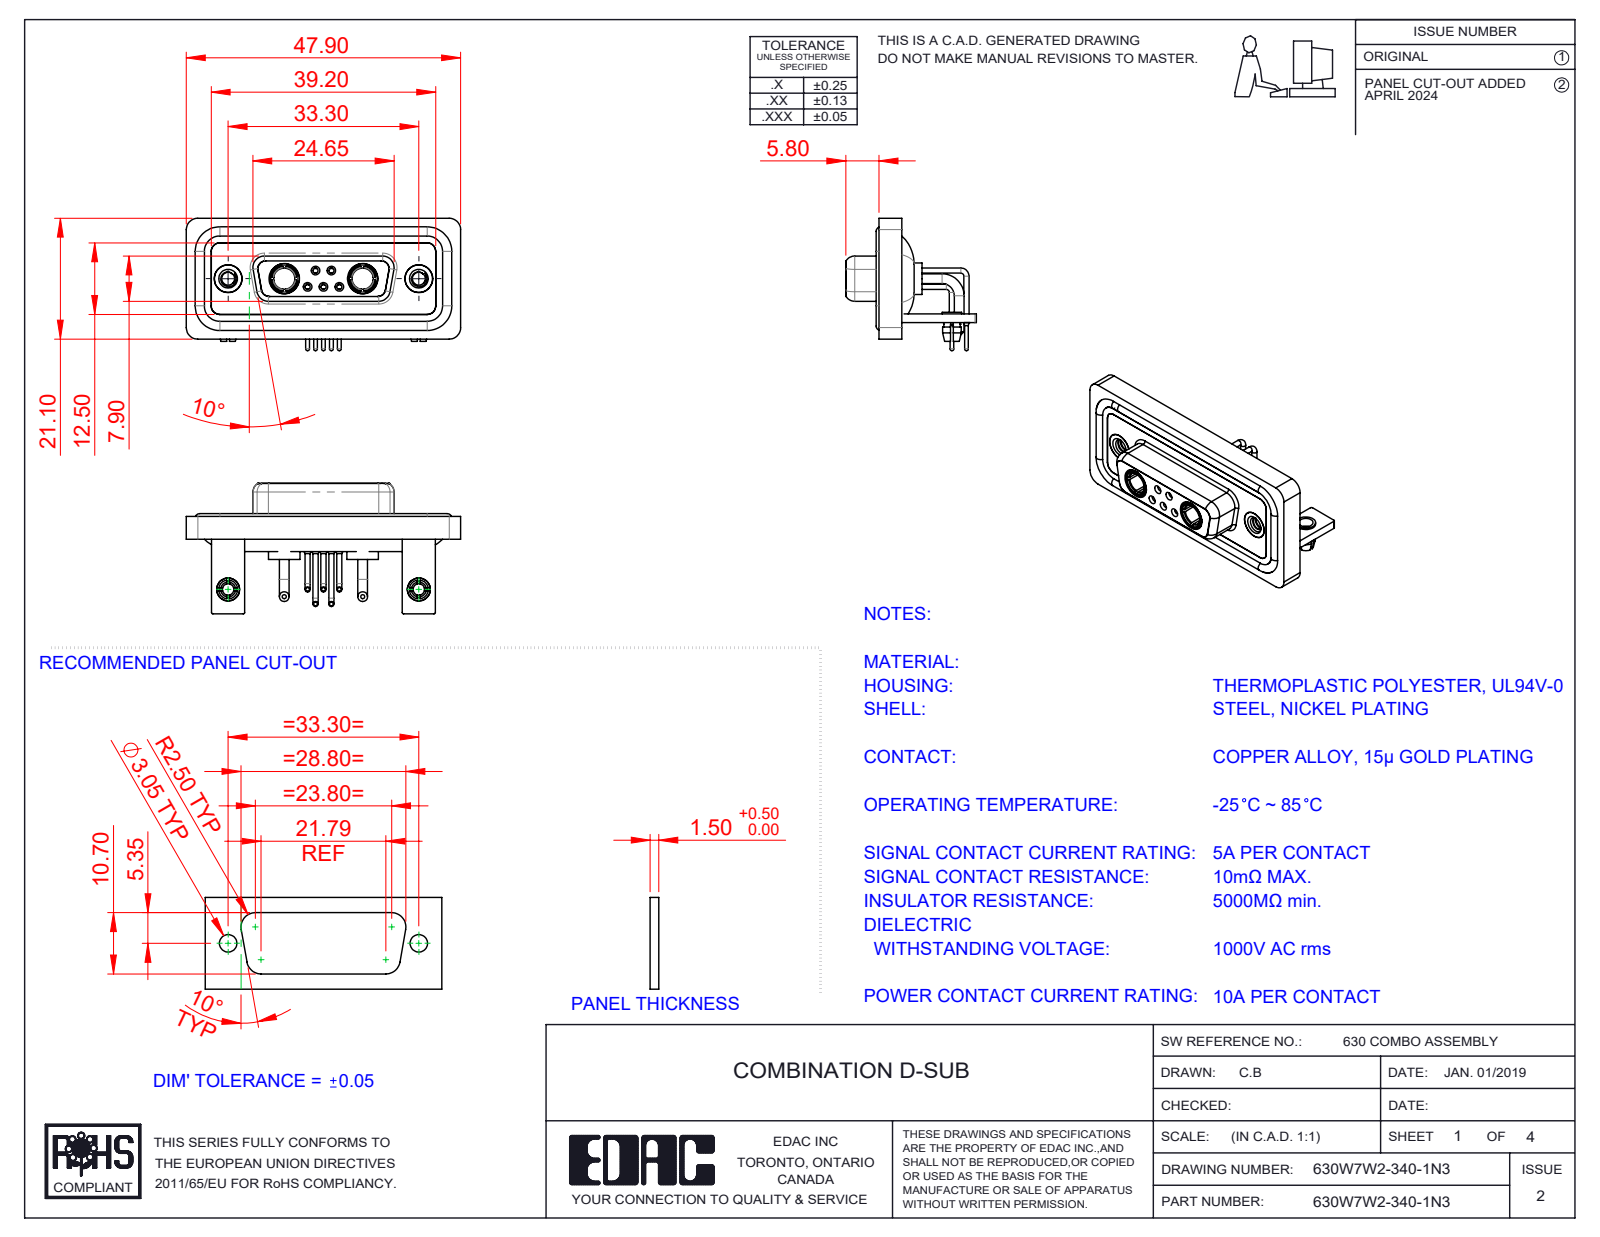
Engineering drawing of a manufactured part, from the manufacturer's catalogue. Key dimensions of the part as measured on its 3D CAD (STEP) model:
Part name (STEP PRODUCT): Power Socket_10A RA; 630Combo Contact Row 2_50 Contacts; 630Combo Housing_7W2; 630Combo Waterproof Housing_15 Contacts (+7 more)
STEP written by: SolidWorks 2023 (CONFIG_CONTROL_DESIGN)
Units: millimetres
Bodies: 20 solids, 947 faces (306 planar, 409 cylindrical, 232 other)
Overall size (bounding box): 47.9 × 23.12 × 22.8
Volume: 6 483 mm³ · Surface area: 11 050 mm²
Round holes (diameter × count): ⌀2 ×7, ⌀0.9 ×5, ⌀1.1 ×5, ⌀1.5 ×5, ⌀4.85 ×4, ⌀1.6 ×3, ⌀1.7 ×2, ⌀2.26 ×2, ⌀2.5 ×2, ⌀3.2 ×2, ⌀3.7 ×2, ⌀4 ×2
Round bosses / shafts (diameter × count): ⌀1.6 ×6, ⌀0.9 ×5, ⌀0.65 ×5, ⌀1.7 ×4, ⌀5.5 ×2, ⌀5.2 ×2, ⌀4.96 ×2, ⌀4.95 ×2
Partial cylindrical surfaces — rounded edges, fillets, slot ends (radius × count): R2 ×21, R1.5 ×18, R0.25 ×16, R1.35 ×12, R1.6 ×8, R0.5 ×5, R0.6 ×4, R0.65 ×4
Main face-to-face distances: 0.4, 2.9, 1.5, 1.8, 3.7, 1.1, 4.1, 1.6, 2.5, 1.4
Hole centre spacings: 3.16, 2.77, 9.8, 23.5, 33.3, 4.31, 4.33, 5.03
